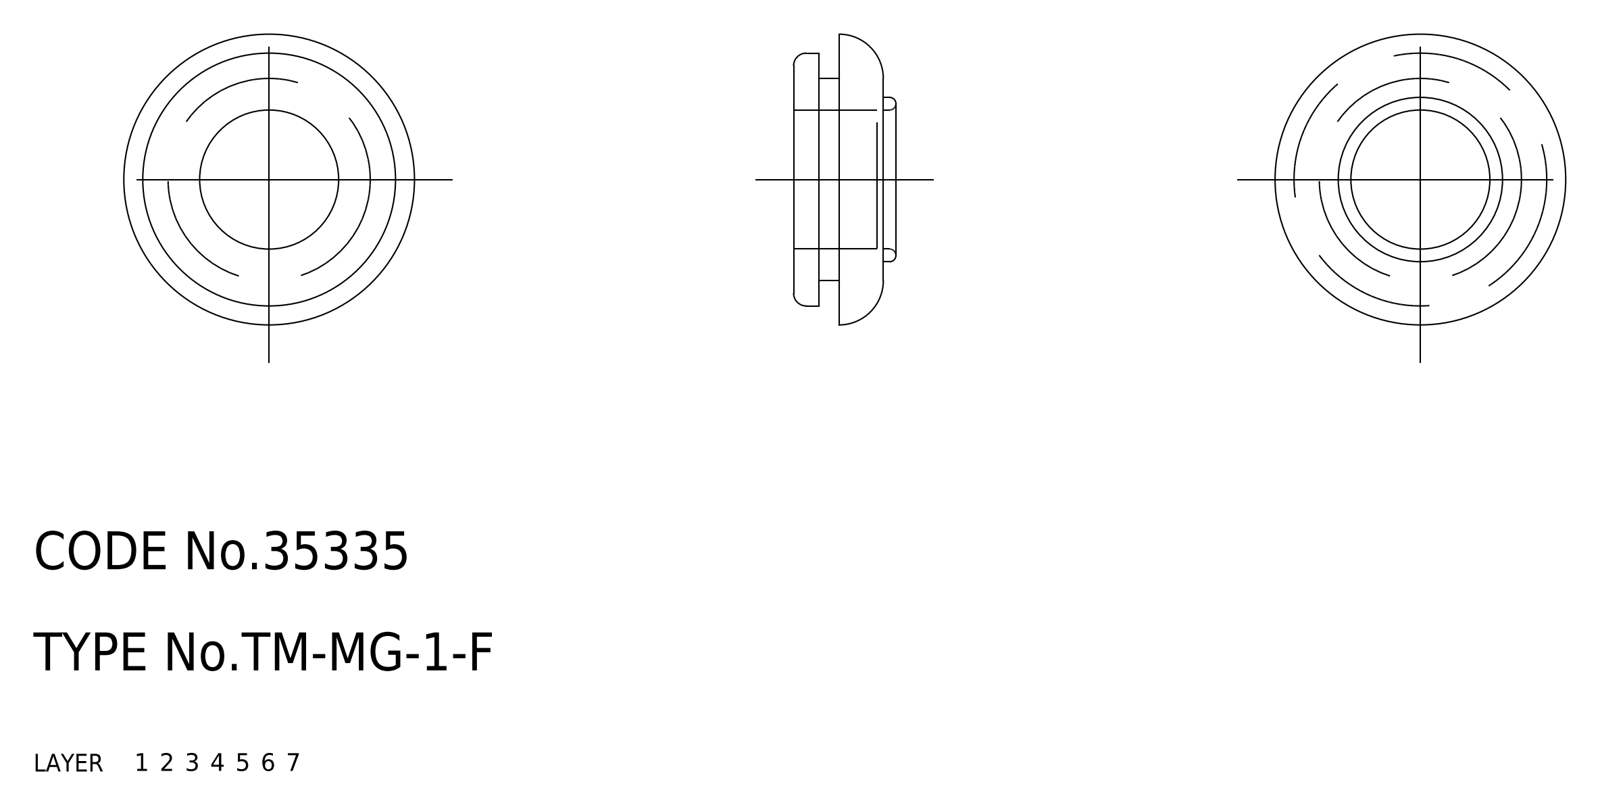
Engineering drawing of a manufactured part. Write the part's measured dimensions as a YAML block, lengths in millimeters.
part_name: "TM_MG_1_F; grommet"
step_written_by: "SolidWorks 2015 (AUTOMOTIVE_DESIGN)"
units: millimeters
bodies: {solids: 1, faces: 22, planar: 6, cylindrical: 10, other: 6}
overall_size: [23, 23, 8.1]
volume: 1620
surface_area: 1662
round_holes:
  - {diameter: 11, count: 1}
round_bosses_or_shafts:
  - {diameter: 20, count: 1}
  - {diameter: 16, count: 1}
  - {diameter: 13, count: 1}
face_to_face_distances: [3.5, 3.6, 7.1, 2, 1.6, 5.1, 6.6, 4.6, 3, 0.5]
